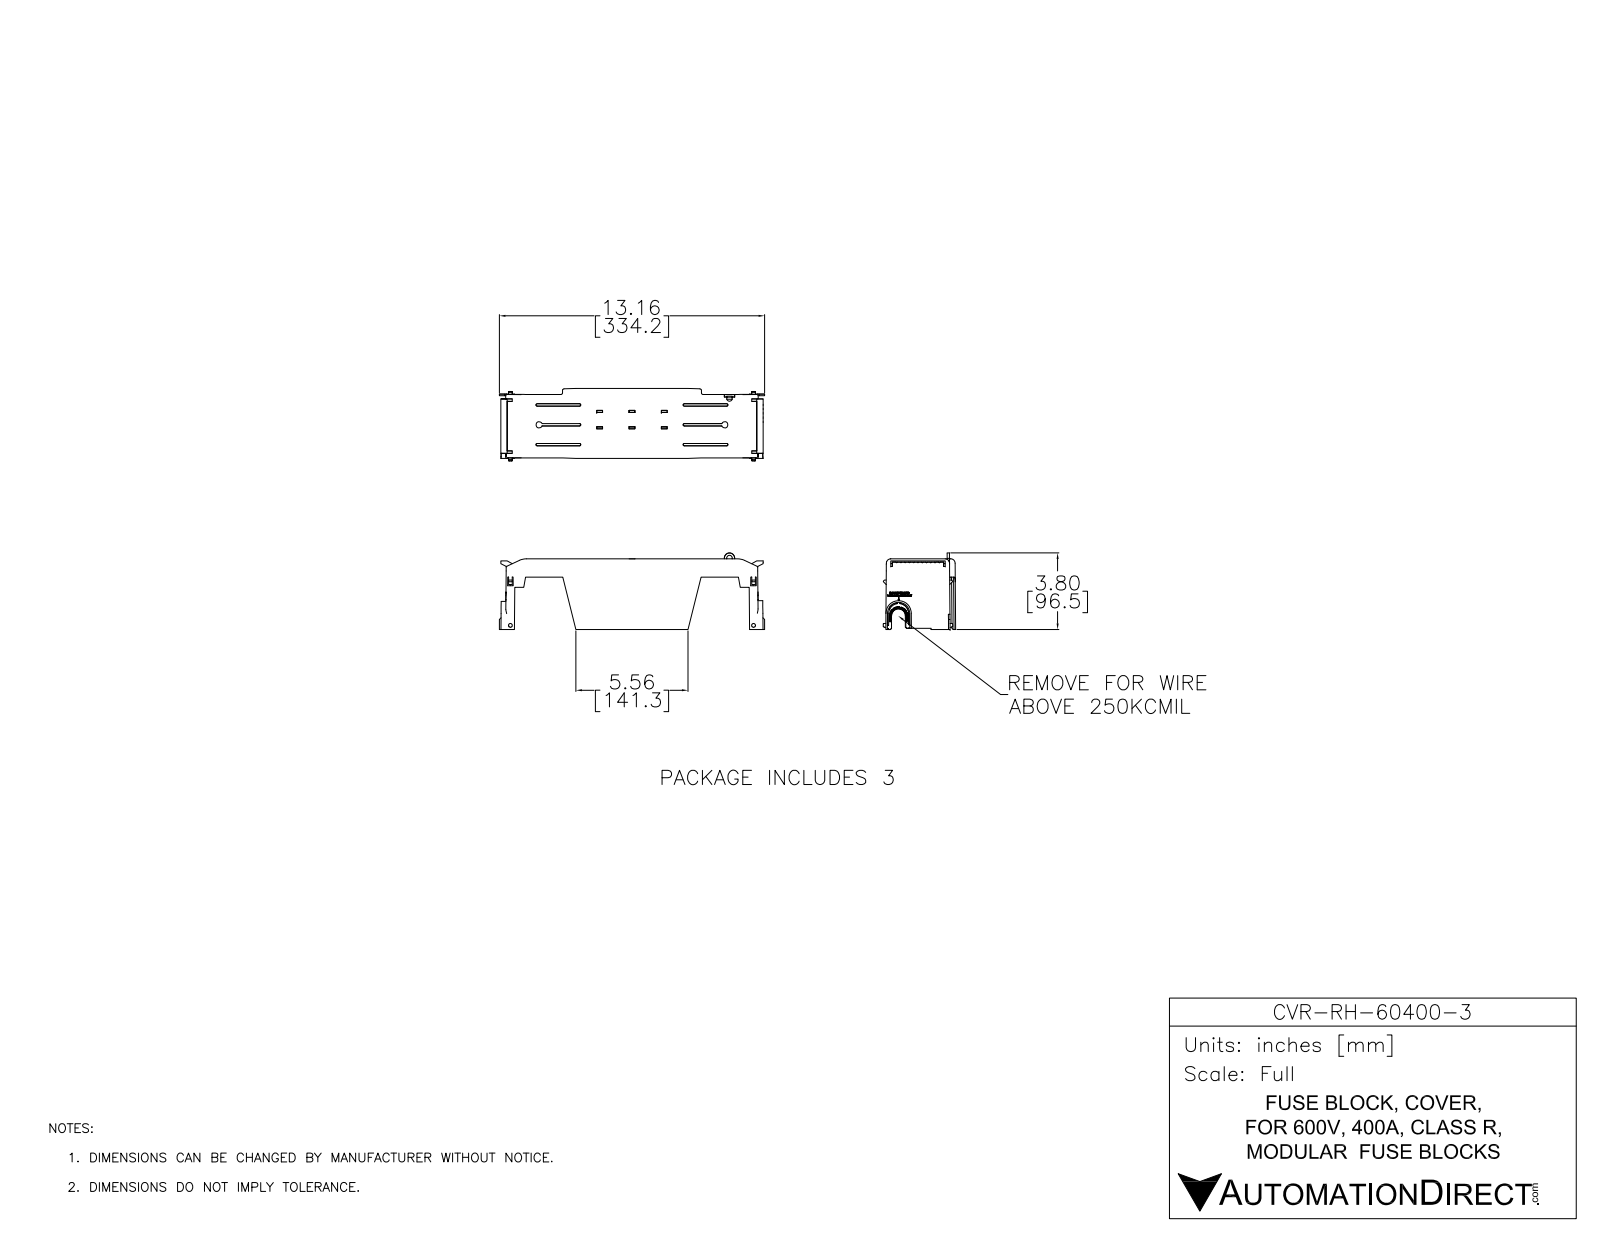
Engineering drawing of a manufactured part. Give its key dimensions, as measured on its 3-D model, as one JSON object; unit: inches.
{"part_name": "CVR-RH-60400-3", "step_written_by": "SolidWorks 2017 (AUTOMOTIVE_DESIGN)", "units": "inches", "bodies": {"solids": 1, "faces": 2374, "planar": 1611, "cylindrical": 104, "other": 659}, "overall_size": [13.158, 3.8, 3.594], "volume_in3": 10.25, "surface_area_in2": 270.7, "round_holes": [[0.276, 1]], "partial_cylinders_radius": [[0.039, 18], [0.079, 8], [0.118, 8], [0.138, 8], [0.217, 8], [0.01, 2], [0.02, 2], [0.04, 2]], "face_to_face_distances": [0.079, 0.276, 0.197, 0.354, 0.118, 0.803, 1.472, 0.669, 0.236, 4.974]}
